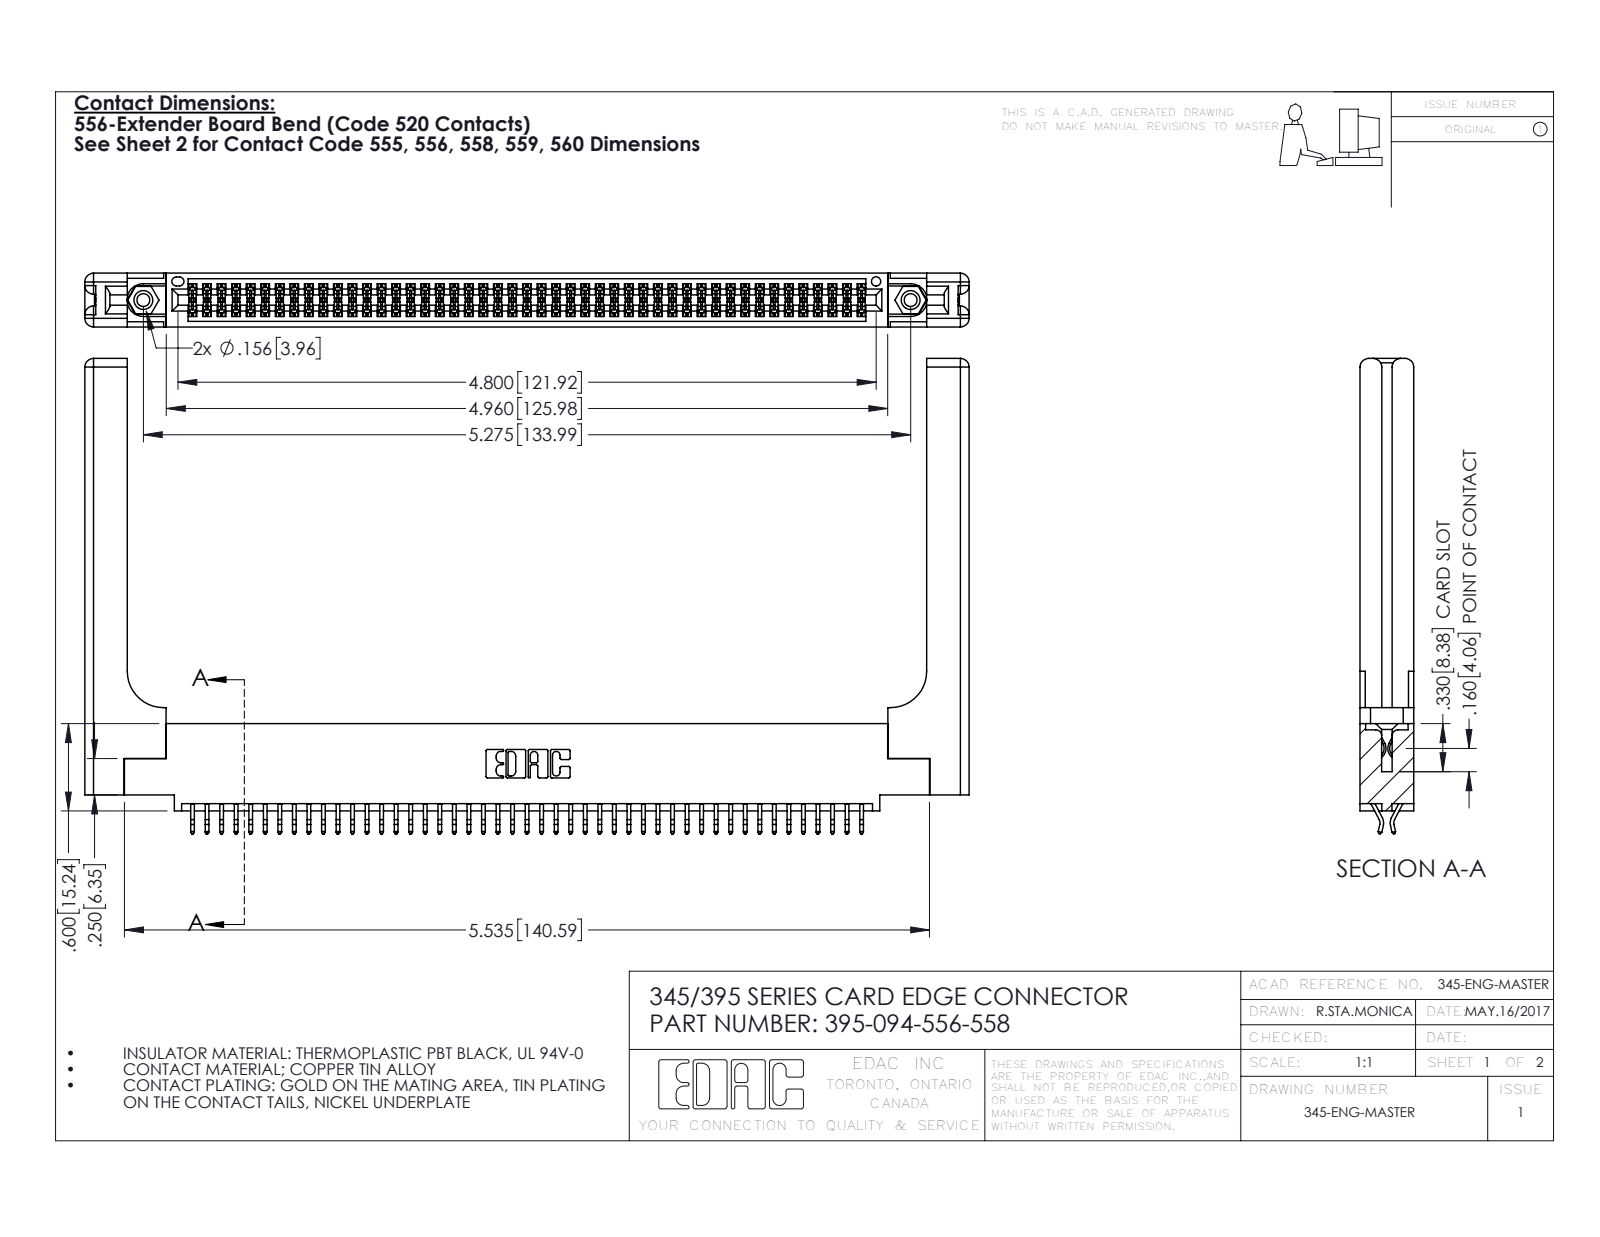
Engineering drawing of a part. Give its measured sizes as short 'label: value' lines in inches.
name: 345-292-001_556 Tail; 345 Part_0.110 Offset - 0.156 Dia-TH; 345-250-001_345-250-001-102; 395-094-556-558 (+1 more)
written by: SolidWorks 2016 (CONFIG_CONTROL_DESIGN)
unit: in
bodies: 99 solids, 5650 faces (3710 planar, 1880 cylindrical, 60 other)
size: 6.079 × 3.267 × 0.37
volume: 1.431 in³; area: 42.3 in²
holes: 2× ⌀0.089, 2× ⌀0.125, 2× ⌀0.156, 1× ⌀0.064
bosses: 2× ⌀0.155
rounds: 141× R0.006, 22× R0.01, 16× R0.06, 6× R0.007, 6× R0.031, 3× R0.026, 2× R0.01, 2× R0.014
face distances: 0.072, 0.37, 0.298, 0.025, 0.098, 0.272, 0.2, 0.225, 0.148, 0.15
hole spacings: 0.27, 5.039, 5.275
